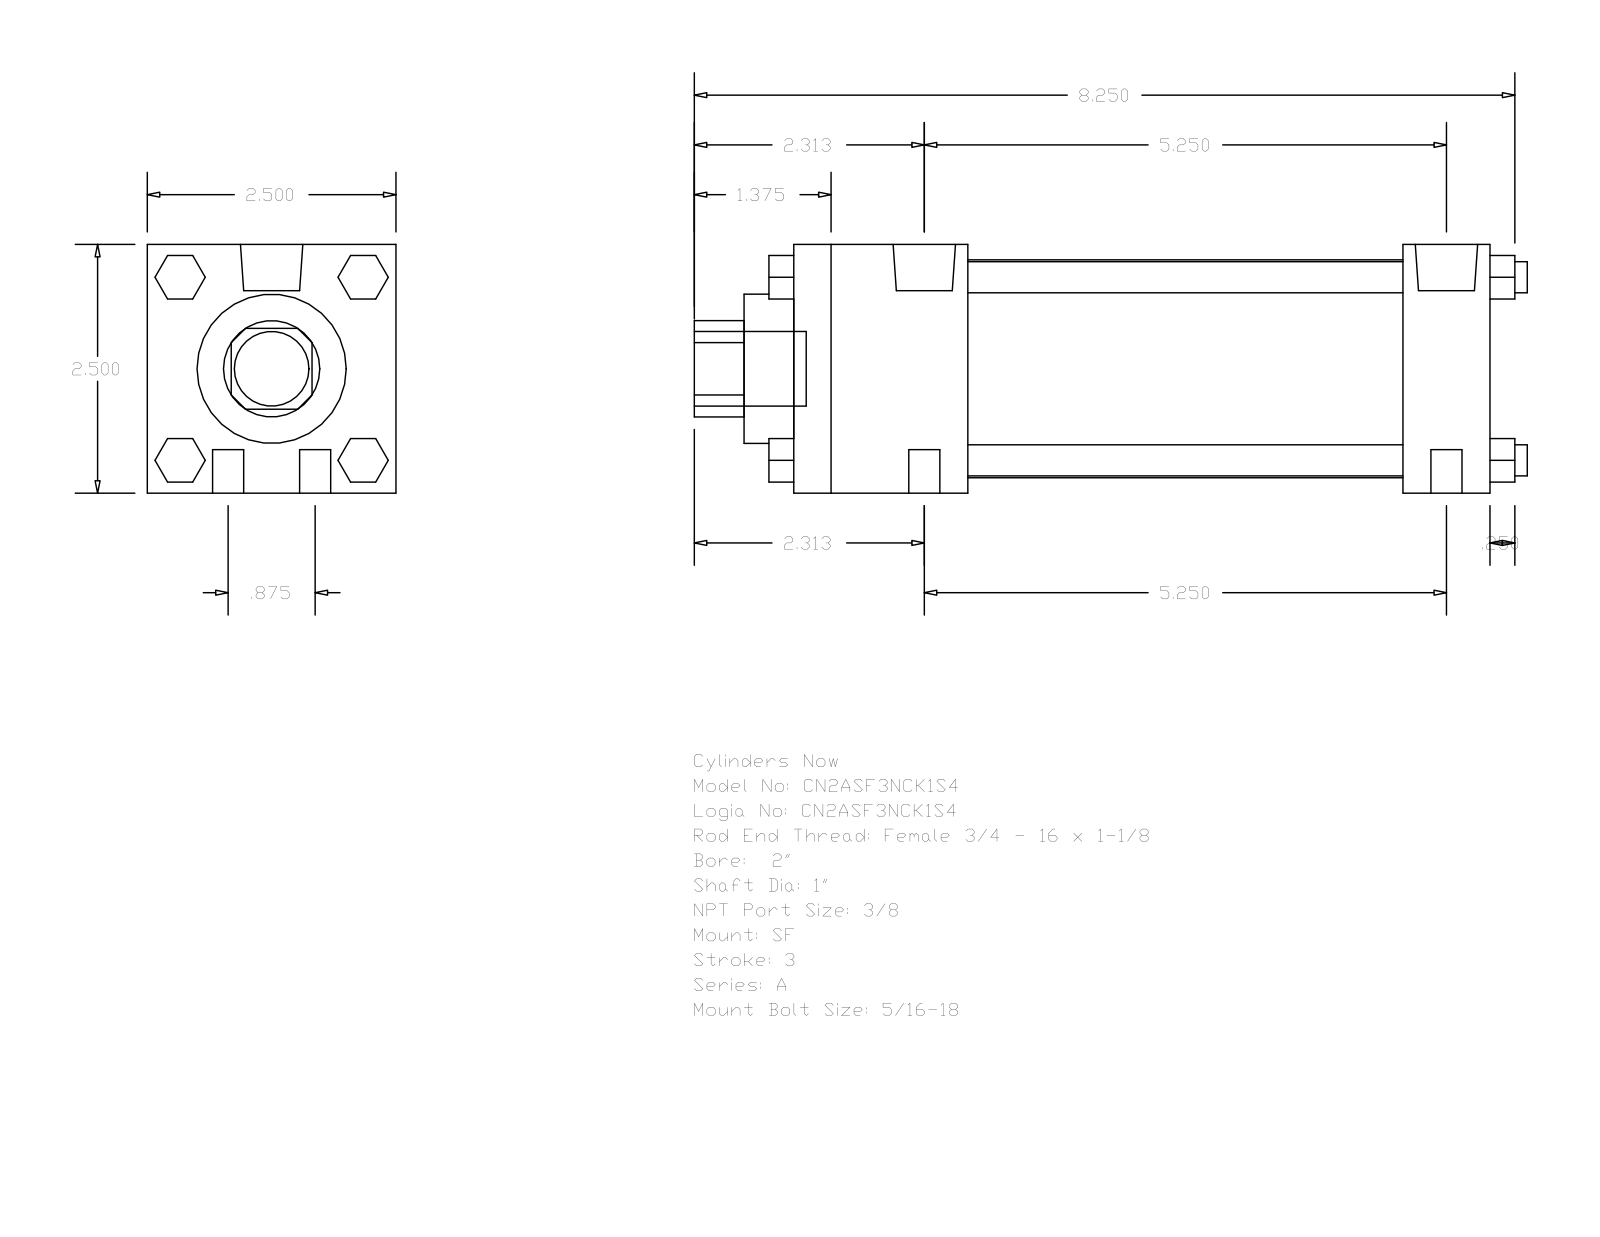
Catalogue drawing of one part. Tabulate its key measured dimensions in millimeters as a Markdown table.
| quantity | value |
| --- | --- |
| part name | A_SF__0200_1 |
| STEP written by | GSSL Pune (CONFIG_CONTROL_DESIGN) |
| units | millimeters |
| bodies | 0 solids, 124 faces (94 planar, 30 cylindrical, 0 other) |
| overall size | 212.72 × 63.5 × 63.5 |
| round holes (diameter × count) | 25.4 × 1, 38.1 × 1, 55.63 × 1 |
| round bosses / shafts (diameter × count) | 7.94 × 8, 15.93 × 2, 5.56 × 2, 19.05 × 1 |
| partial cylindrical surfaces (radius × count) | 12.29 × 1 |
| main face-to-face distances | 63.5, 177.8, 155.57, 22.23, 44.45, 111.12, 133.35, 12.7, 190.5, 6.35 |
